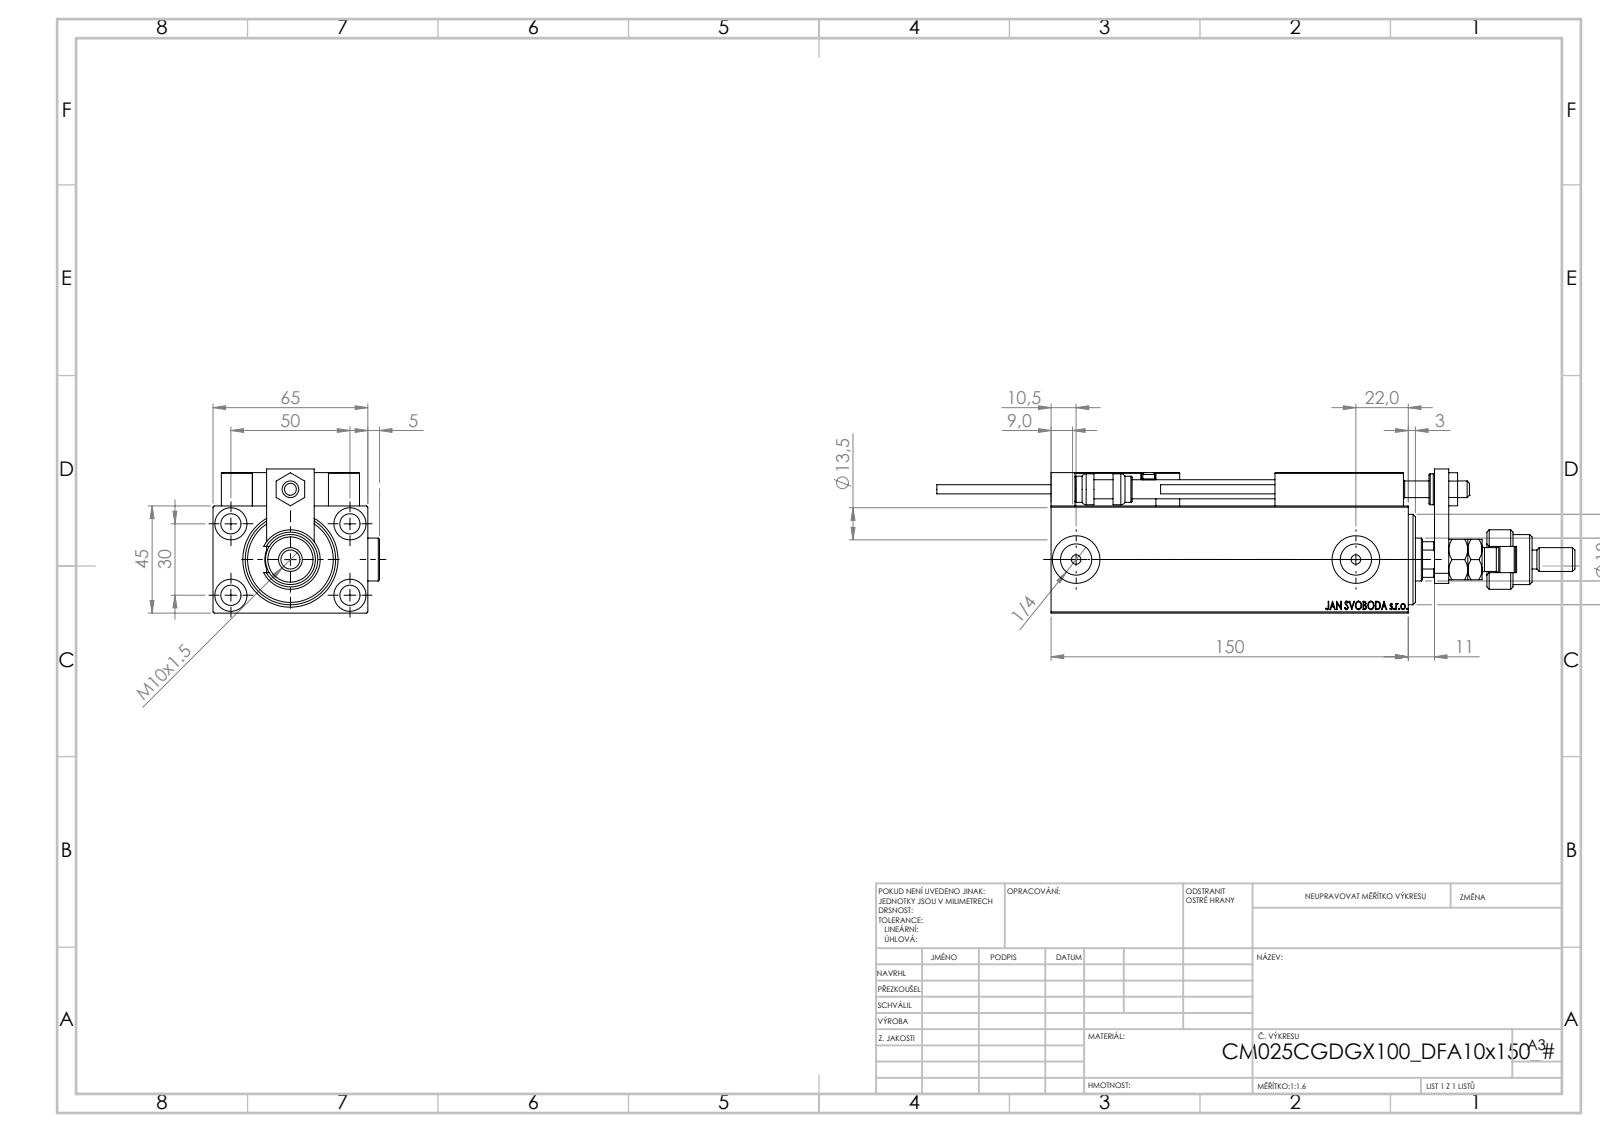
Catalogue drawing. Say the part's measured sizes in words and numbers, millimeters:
The part is named "SWITCH DIM B,W; V450CM_VC_B; V450CM_C_VCP; Zatka_OIL_PORT (+7 more)". Its 3-D file was written by "SolidWorks 2019 (CONFIG_CONTROL_DESIGN)". It is 27 solids with 1421 faces: 622 planar, 217 cylindrical and 582 other. Overall it measures 268 by 69.9 by 60.5 millimeters. Its volume is 434 340 cubic millimeters and its surface area 116 389 square millimeters. Round holes: 6 of diameter 4, 5 of diameter 8, 5 of diameter 8.5, 4 of diameter 3.2, 4 of diameter 13.5, 2 of diameter 5, 2 of diameter 13.16, 2 of diameter 20, 1 of diameter 7, 1 of diameter 14.5, 1 of diameter 18, 1 of diameter 21.5. Round bosses or shafts: 2 of diameter 18, 2 of diameter 5, 2 of diameter 3.8, 1 of diameter 25, 1 of diameter 21, 1 of diameter 16, 1 of diameter 13, 1 of diameter 11. Partial cylindrical surfaces (rounded edges, fillets, slot ends): 30 of radius 0.3, 2 of radius 3, 1 of radius 5.5, 1 of radius 8.5, 1 of radius 8.75. The main face-to-face distances are 45, 65, 14, 6, 59, 3, 5, 13, 7, 161. The hole center spacings are 29.15, 11.37, 20, 28.9, 29.59, 29.69, 30, 36.06.
